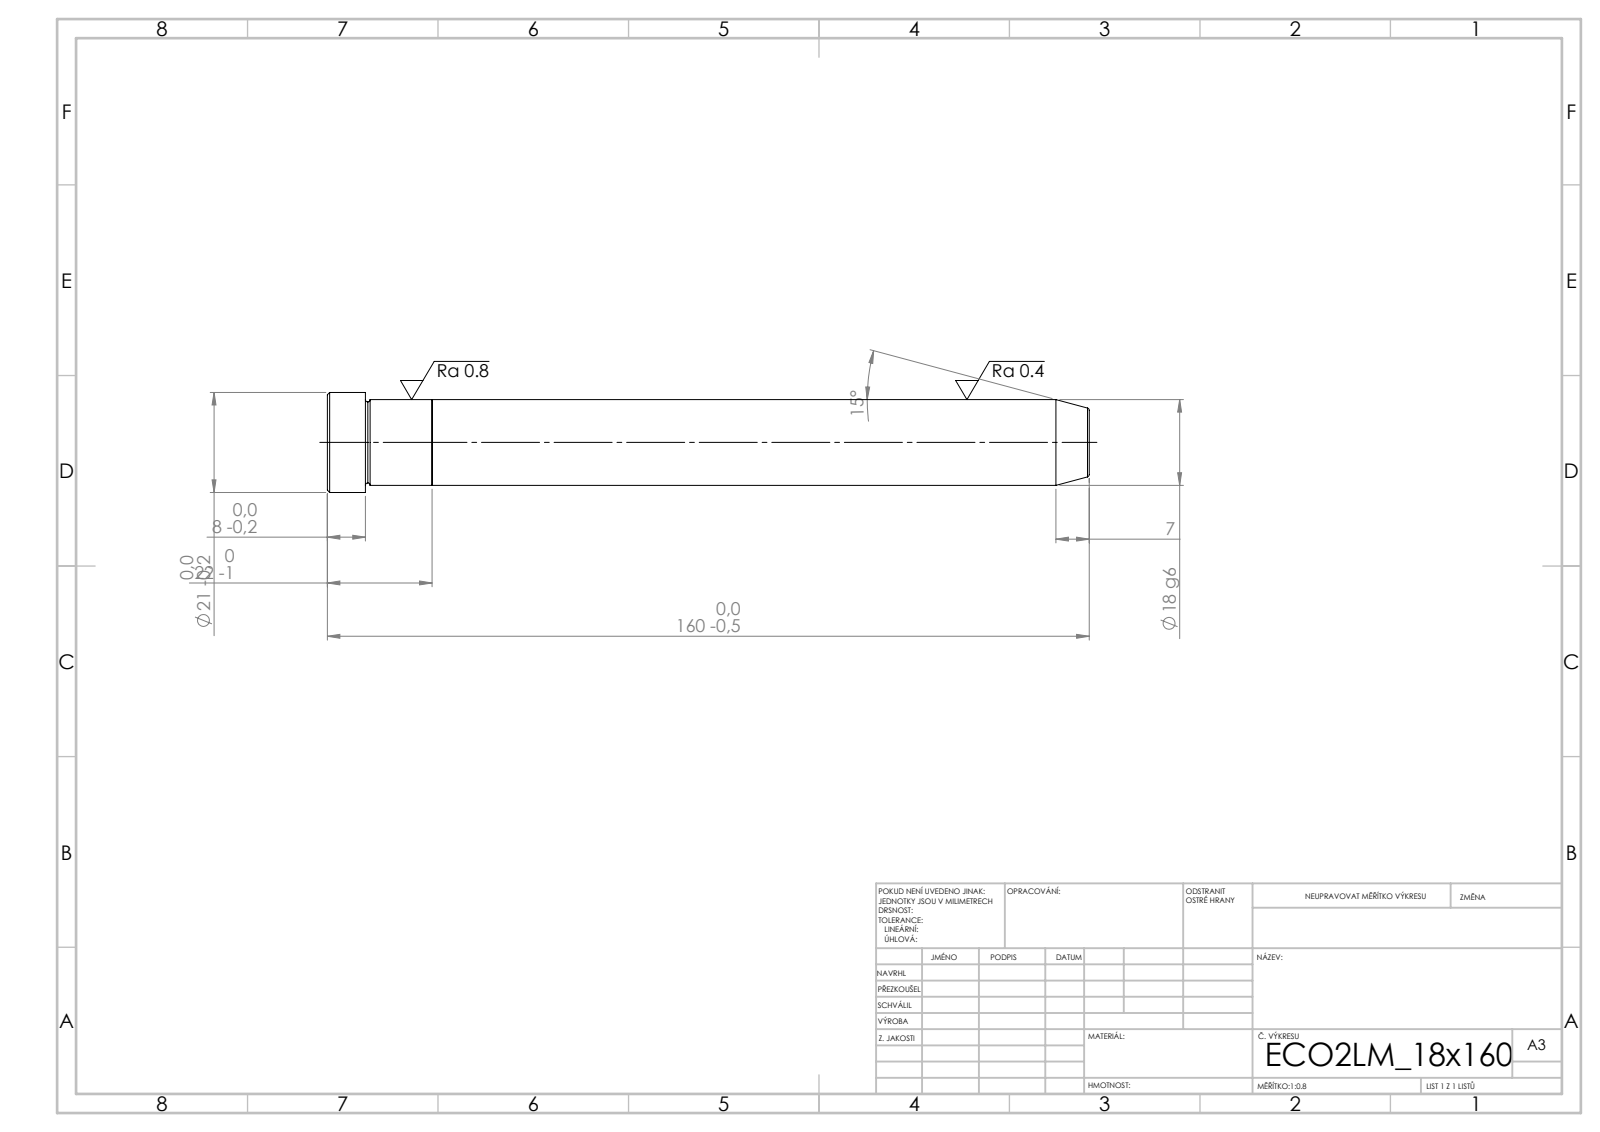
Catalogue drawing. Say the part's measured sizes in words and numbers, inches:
Its 3-D file was written by "SolidWorks 2019 (CONFIG_CONTROL_DESIGN)". It is 2 solids with 21 faces: 5 planar, 6 cylindrical and 10 other. Overall it measures 6.299 by 0.827 by 0.827 inches. Its volume is 2.506 cubic inches and its surface area 15.82 square inches. Round bosses or shafts: 1 of diameter 0.827, 1 of diameter 0.709. The main face-to-face distances are 0.866, 5.433, 6.299, 5.984, 0.551, 0.315.
